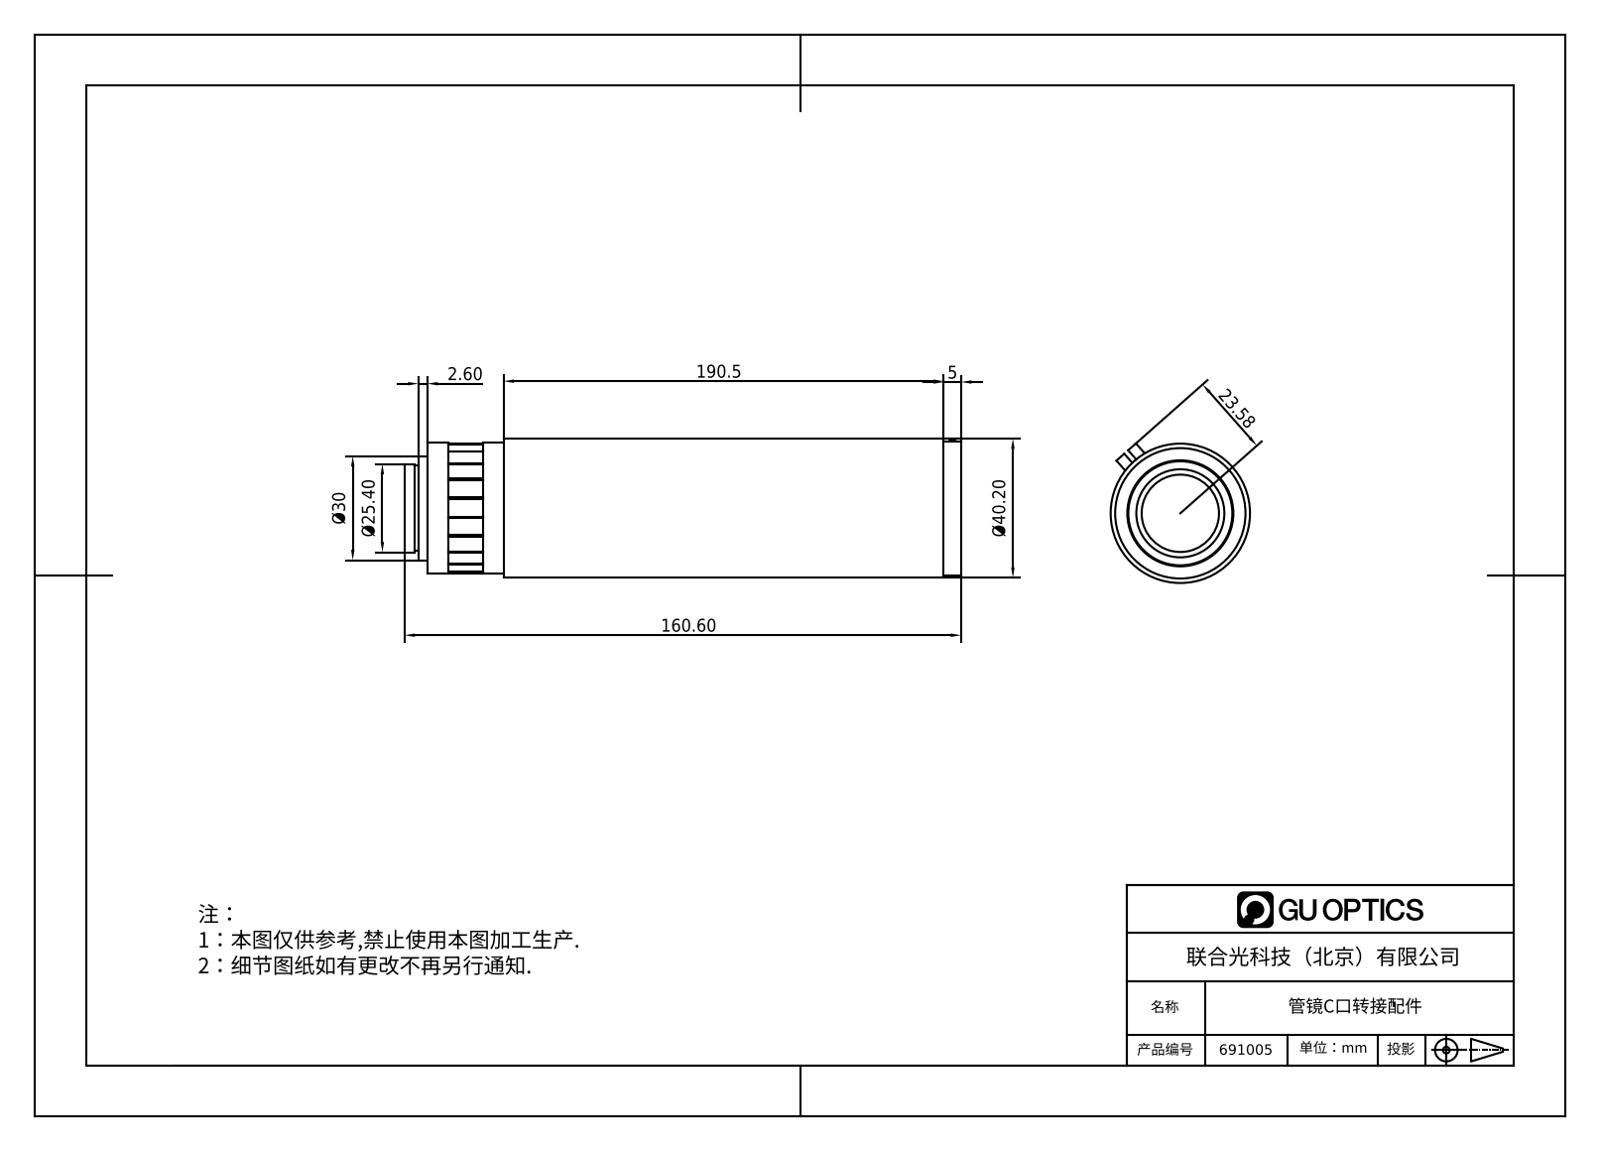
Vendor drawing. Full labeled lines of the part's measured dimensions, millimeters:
Part name (STEP PRODUCT): 691005
STEP written by: SolidWorks 2020 (CONFIG_CONTROL_DESIGN)
Units: millimetres
Bodies: 5 solids, 135 faces (61 planar, 71 cylindrical, 3 other)
Overall size (bounding box): 160.59 × 40.26 × 40.2
Volume: 57 359 mm³ · Surface area: 47 033 mm²
Round holes (diameter × count): ⌀1.25 ×1, ⌀1.6 ×1, ⌀2.05 ×1, ⌀2.2 ×1, ⌀22.3 ×1, ⌀27 ×1, ⌀30 ×1, ⌀30.6 ×1, ⌀31.6 ×1, ⌀32.6 ×1, ⌀34 ×1, ⌀35.6 ×1
Round bosses / shafts (diameter × count): ⌀40.2 ×1, ⌀38.62 ×1, ⌀37.6 ×1, ⌀25.4 ×1, ⌀24.6 ×1
Partial cylindrical surfaces — rounded edges, fillets, slot ends (radius × count): R10.5 ×21, R1.5 ×4
Main face-to-face distances: 16, 6, 5, 149, 8.59, 1, 10, 19, 7.59, 148
